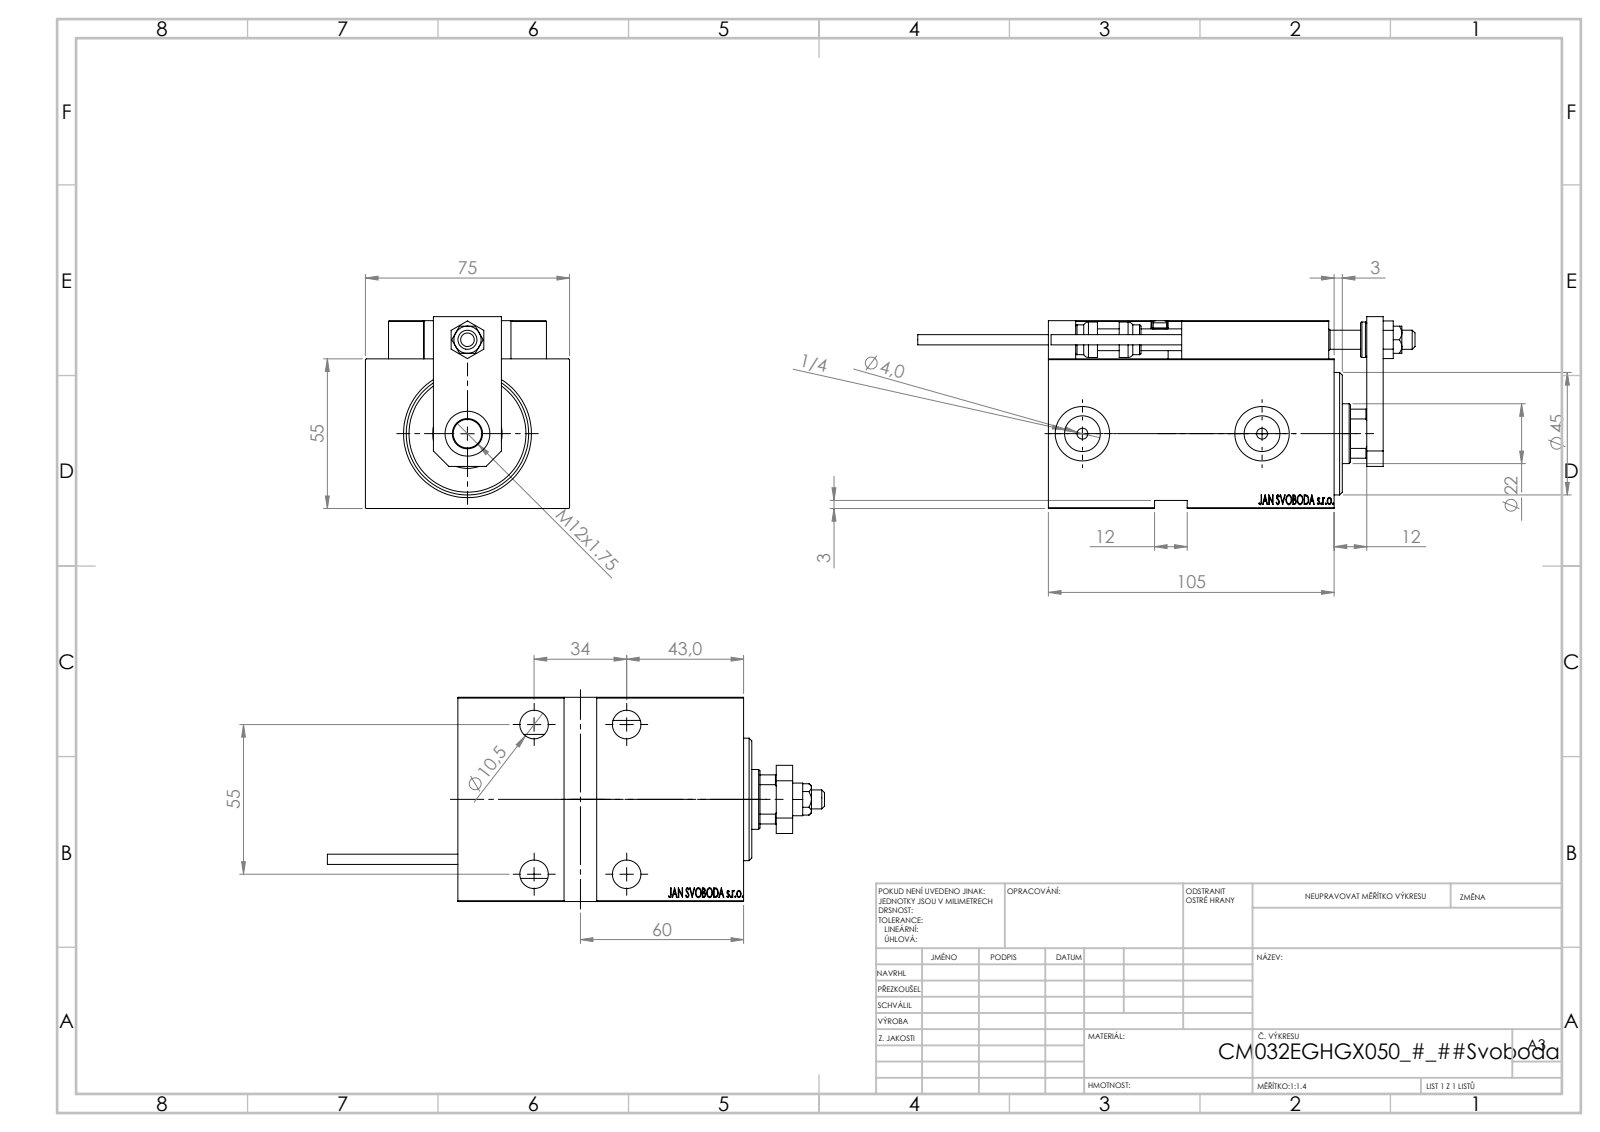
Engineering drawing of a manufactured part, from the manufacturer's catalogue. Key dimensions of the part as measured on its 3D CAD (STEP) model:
Part name (STEP PRODUCT): V450CM_E_Body; TYC_L79; KONCOVKA; Block (+7 more)
STEP written by: SolidWorks 2019 (CONFIG_CONTROL_DESIGN)
Units: millimetres
Bodies: 24 solids, 1290 faces (569 planar, 180 cylindrical, 541 other)
Overall size (bounding box): 182.7 × 75 × 70.5
Volume: 436 291 mm³ · Surface area: 96 491 mm²
Round holes (diameter × count): ⌀4 ×6, ⌀8 ×5, ⌀10.5 ×5, ⌀16.5 ×5, ⌀3.2 ×4, ⌀5 ×2, ⌀13.16 ×2, ⌀20 ×2, ⌀7 ×1, ⌀22 ×1, ⌀25.5 ×1, ⌀32 ×1
Round bosses / shafts (diameter × count): ⌀5 ×2, ⌀3.8 ×2, ⌀34 ×1, ⌀13 ×1, ⌀11 ×1
Partial cylindrical surfaces — rounded edges, fillets, slot ends (radius × count): R0.3 ×30, R3 ×2, R10.5 ×1
Main face-to-face distances: 55, 75, 10, 3, 14, 69, 105, 5, 12, 95
Hole centre spacings: 11.37, 20, 28.9, 29.59, 29.69, 34, 36.06, 40.03
